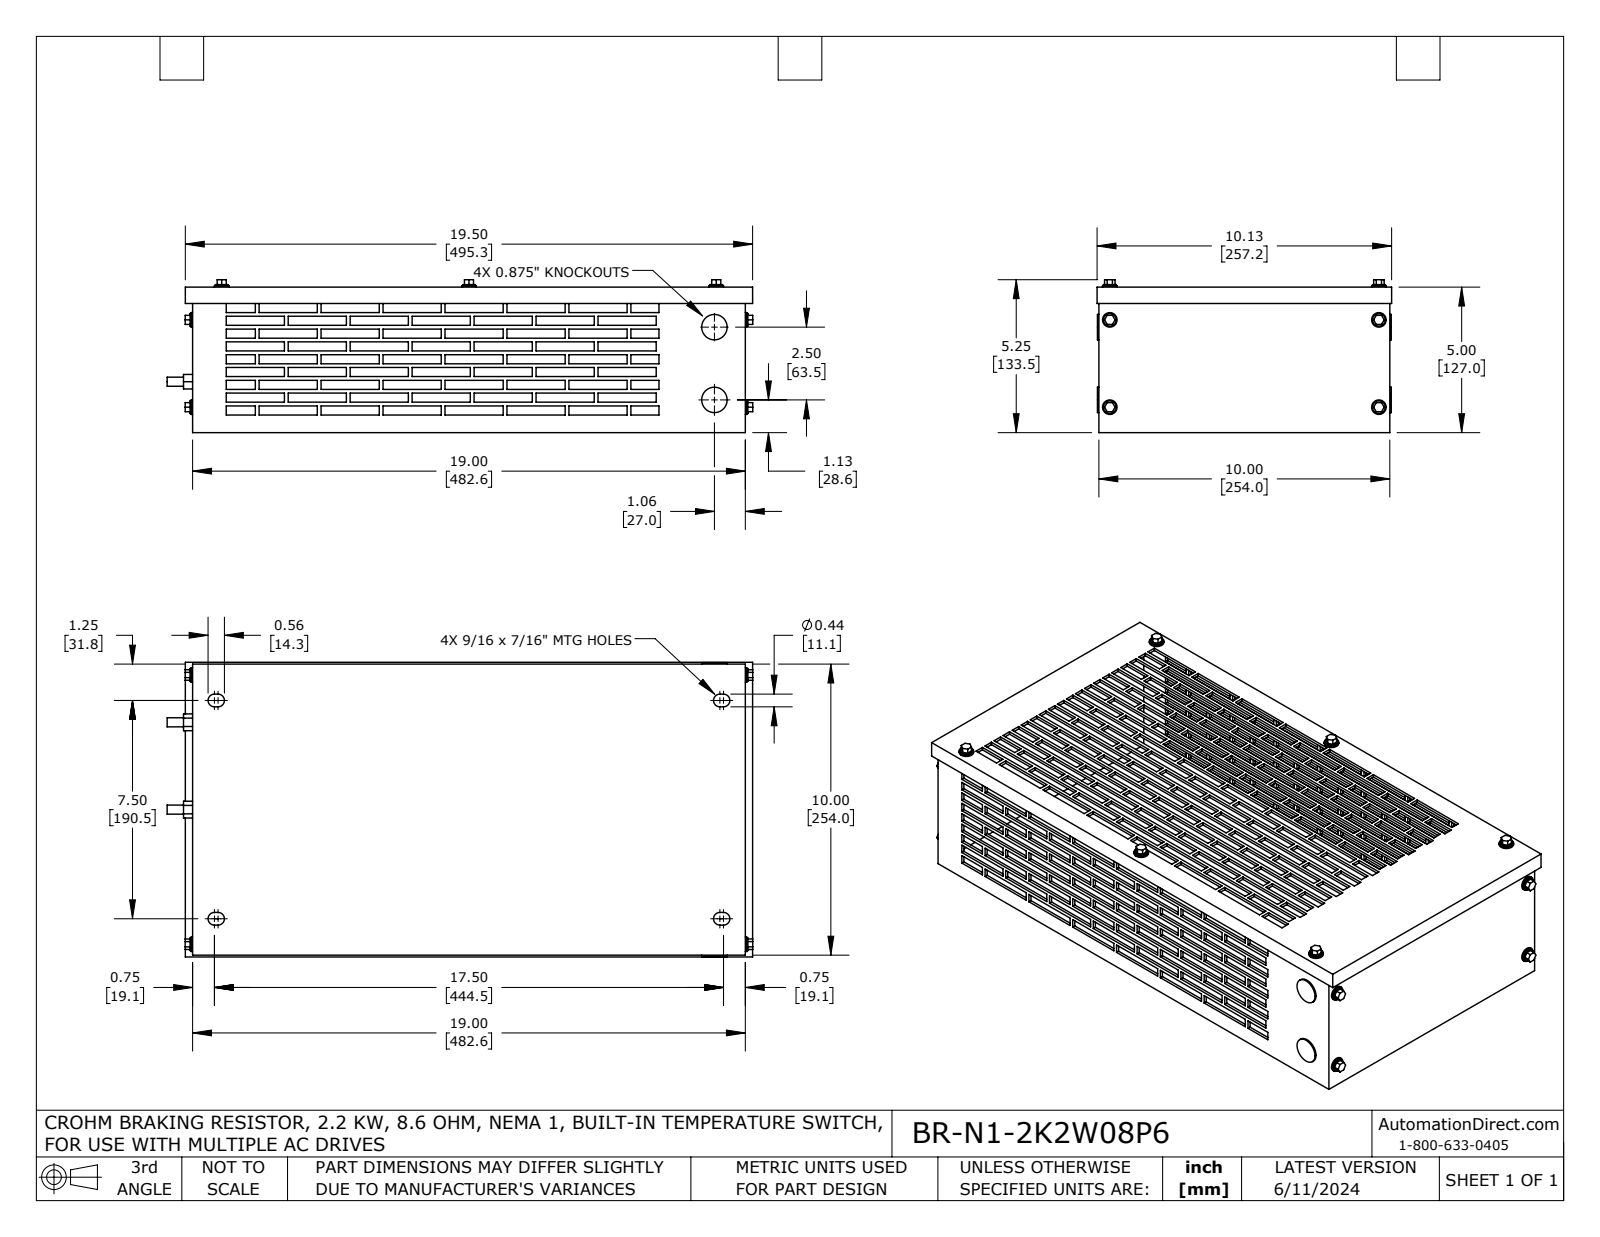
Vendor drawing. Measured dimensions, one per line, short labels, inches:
name: BR-N1-2K2W08P6
written by: SolidWorks 2021 (AUTOMOTIVE_DESIGN)
unit: in
bodies: 35 solids, 1454 faces (1342 planar, 112 cylindrical, 0 other)
size: 20.129 × 10.125 × 5.254
volume: 51.07 in³; area: 1 155 in²
holes: 10× ⌀0.25, 2× ⌀0.75
bosses: 10× ⌀0.5, 10× ⌀0.437, 2× ⌀0.875, 2× ⌀0.313
rounds: 8× R0.219
face distances: 0.1, 4.9, 5, 4.8, 18.9, 9.9, 10, 19, 18.8, 9.8
hole spacings: 9.25, 8.5, 12.562, 3, 9.724, 17, 19.354, 2.5
